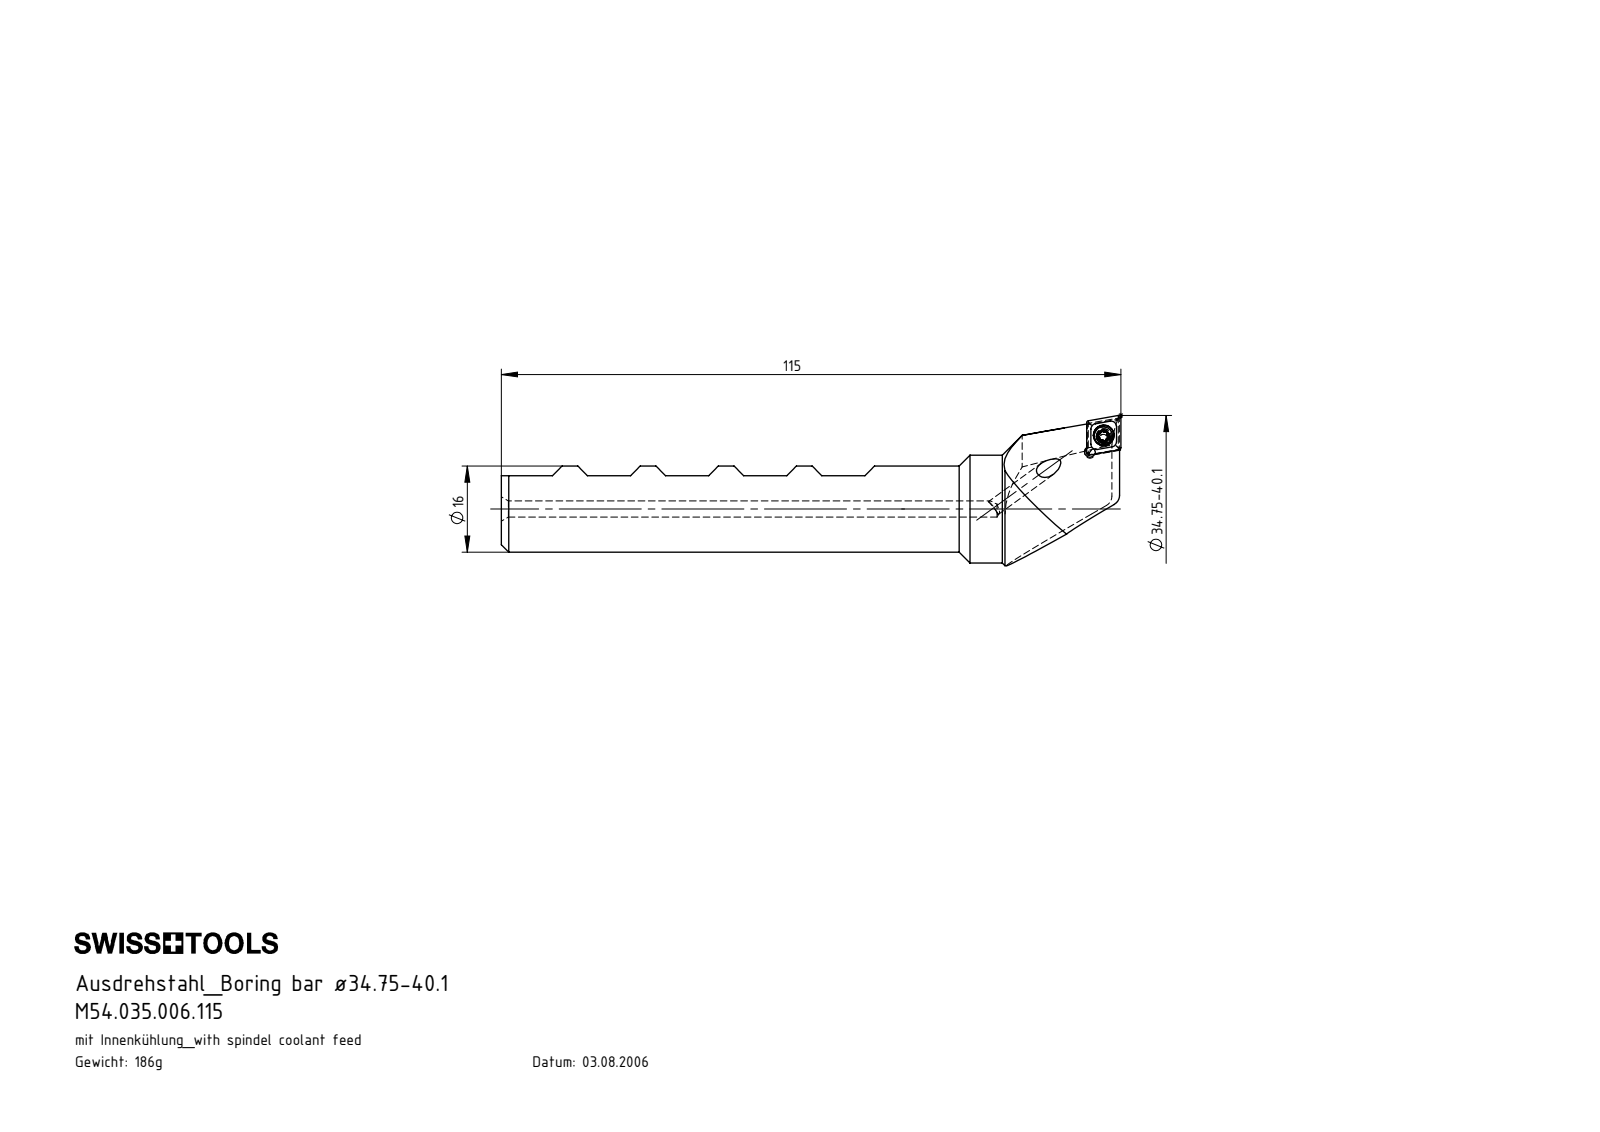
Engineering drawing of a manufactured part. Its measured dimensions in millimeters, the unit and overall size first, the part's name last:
Units: millimetres
Overall size (bounding box): 115 × 27.88 × 22.08
Round holes (diameter × count): ⌀3 ×2, ⌀2 ×1, ⌀2.05 ×1, ⌀2.8 ×1, ⌀3.85 ×1
Round bosses / shafts (diameter × count): ⌀20 ×1, ⌀16 ×1, ⌀3.4 ×1, ⌀2.5 ×1
Partial cylindrical surfaces — rounded edges, fillets, slot ends (radius × count): R0.21 ×6, R0.36 ×5, R0.36 ×1, R2 ×1, R10.5 ×1, R12 ×1
Main face-to-face distances: 10.25, 11.81, 9.63, 2.18, 20.5, 30.76, 20.51, 30.75, 10.26, 41.01
Hole centre spacings: 3.89, 3.99
Volume: 23 662 mm³ · Surface area: 7 817 mm²
Bodies: 3 solids, 106 faces (42 planar, 25 cylindrical, 39 other)
Part name (STEP PRODUCT): WCA-ER2.001.006_A; B35-WCA.K11.115_A; CCMT060204; B35.WCA.K11.115
STEP written by: SolidWorks 2017 (AUTOMOTIVE_DESIGN)
